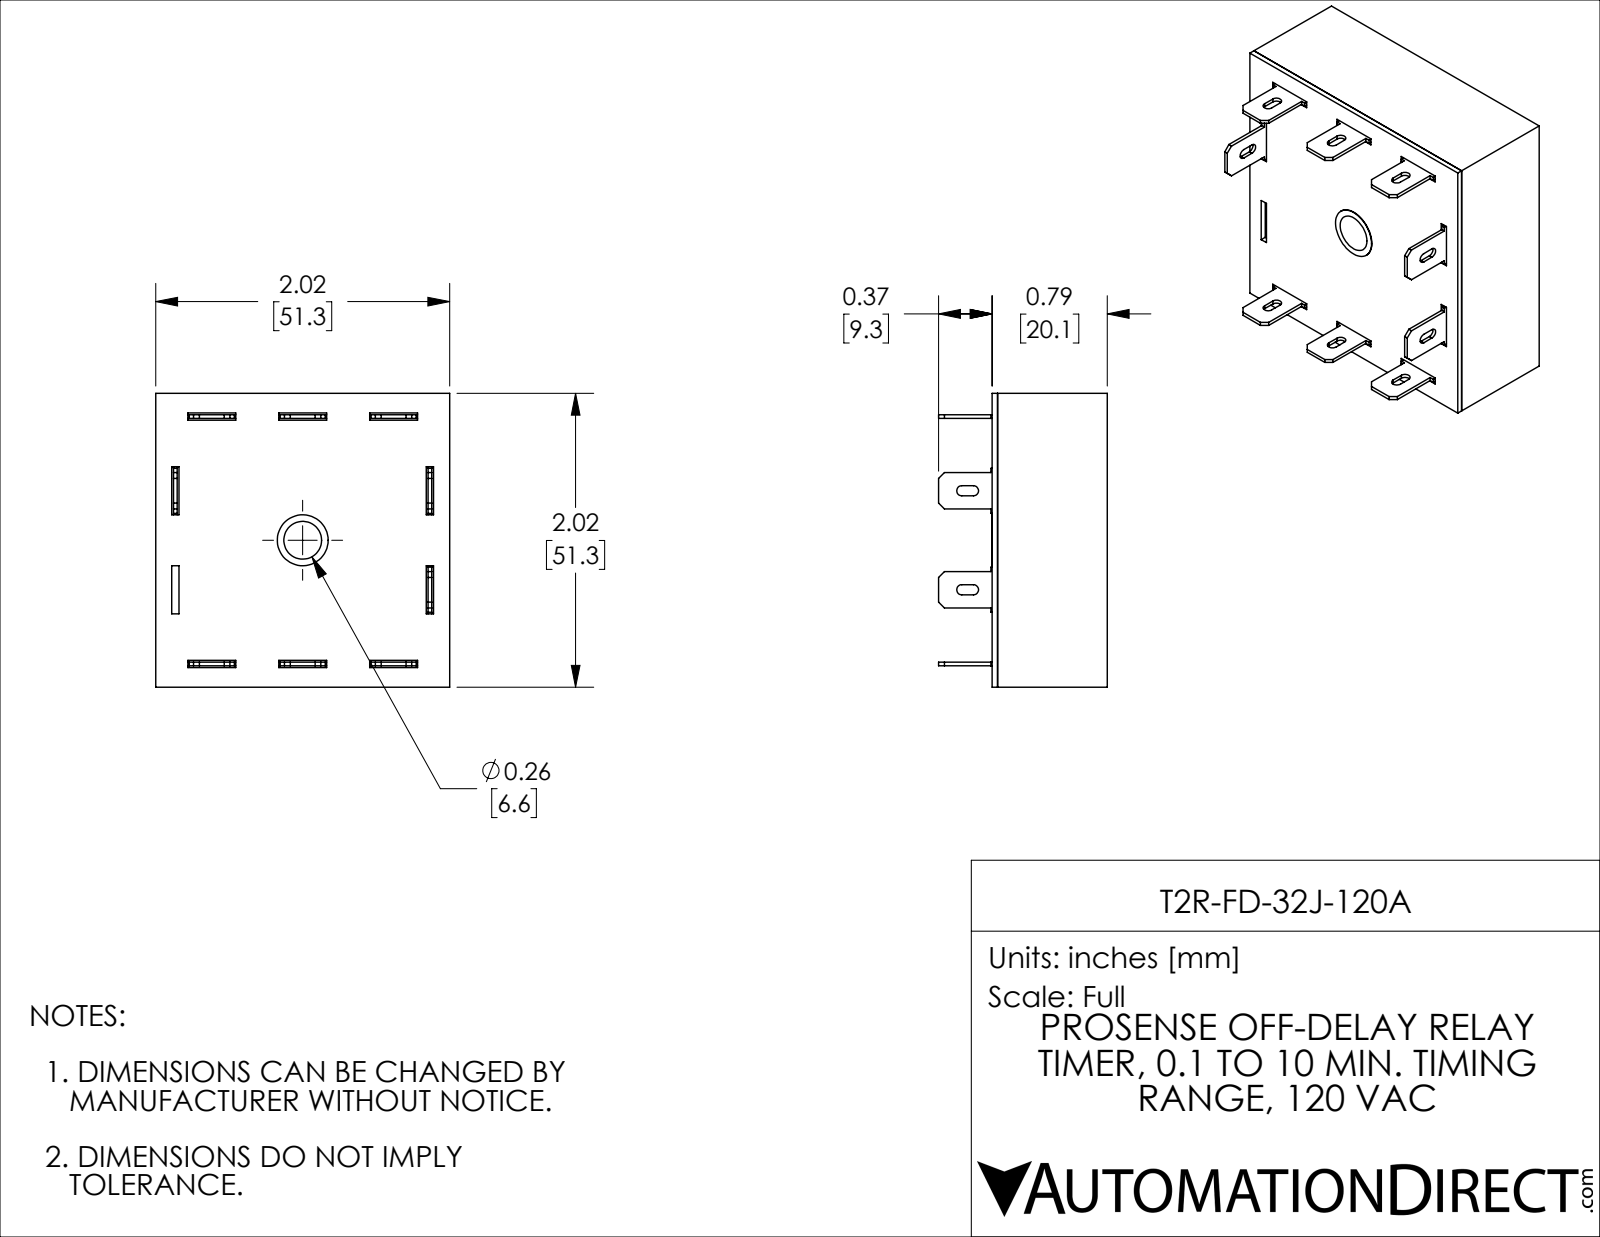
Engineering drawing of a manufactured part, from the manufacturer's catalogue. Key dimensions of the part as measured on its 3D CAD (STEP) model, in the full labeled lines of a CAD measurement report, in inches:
Part name (STEP PRODUCT): T2R-FD-32J-120A
STEP written by: SolidWorks 2021 (CONFIG_CONTROL_DESIGN)
Units: inches
Bodies: 11 solids, 280 faces (256 planar, 22 cylindrical, 2 other)
Overall size (bounding box): 2.02 × 2.02 × 1.16
Volume: 0.682 in³ · Surface area: 36.12 in²
Round holes (diameter × count): ⌀0.35 ×1
Partial cylindrical surfaces — rounded edges, fillets, slot ends (radius × count): R0.035 ×10
Main face-to-face distances: 0.045, 1.975, 0.754, 0.792, 0.038, 0.709, 0.747, 2.02, 0.147, 1.872
